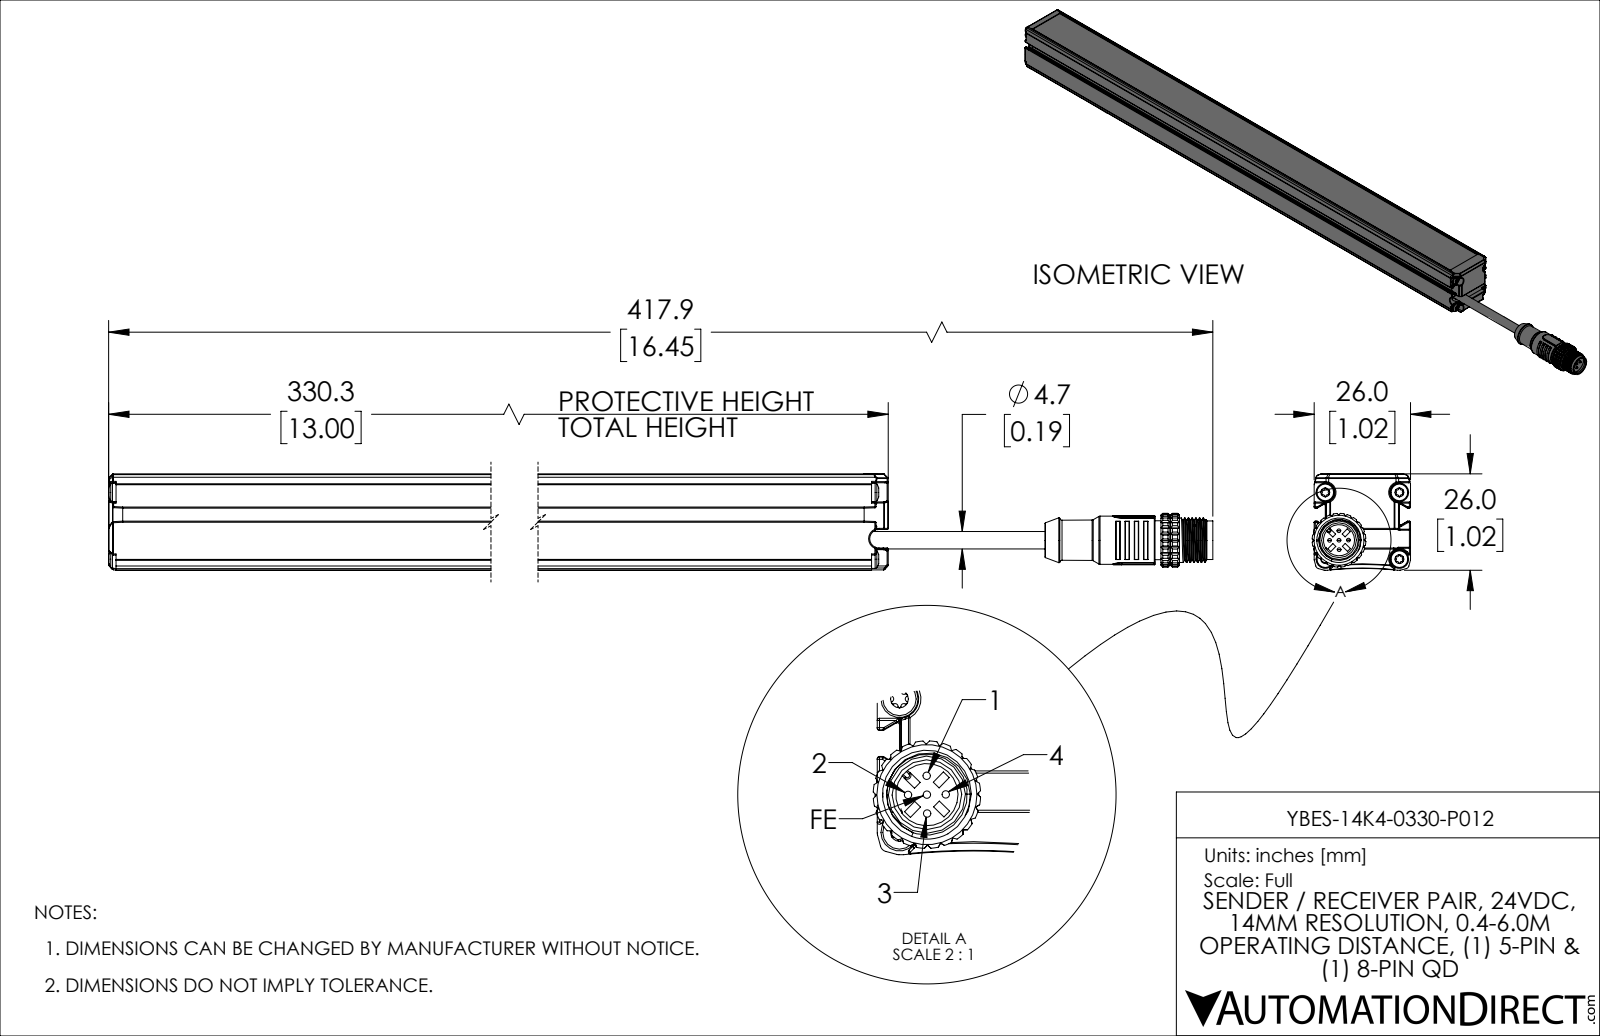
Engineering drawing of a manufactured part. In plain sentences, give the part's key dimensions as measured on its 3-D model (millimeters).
The part is named "YBES-14K4-0330-P012_REV1". Its 3-D file was written by "SolidWorks 2019 (AUTOMOTIVE_DESIGN)". It is 2 solids with 1937 faces: 729 planar, 727 cylindrical and 481 other. Overall it measures 417.9 by 26.5 by 26 millimeters. Its volume is 82 070 cubic millimeters and its surface area 89 030 square millimeters. Round holes: 4 of diameter 2.4, 4 of diameter 2.5, 4 of diameter 3.7, 4 of diameter 5, 1 of diameter 4.8, 1 of diameter 5.9, 1 of diameter 8.4, 1 of diameter 9, 1 of diameter 9.6. Round bosses or shafts: 5 of diameter 1, 5 of diameter 0.9, 4 of diameter 3.2, 4 of diameter 2.5, 4 of diameter 1.3, 2 of diameter 1.5, 1 of diameter 13.5, 1 of diameter 13. Partial cylindrical surfaces (rounded edges, fillets, slot ends): 153 of radius 0.2, 115 of radius 0.3, 24 of radius 0.2, 24 of radius 0.4, 18 of radius 1, 16 of radius 0.4, 10 of radius 0.2, 7 of radius 0.5. The main face-to-face distances are 3, 1.5, 1.8, 21.2, 26, 18.2, 1.2, 0.4, 23, 4.8. The hole center spacings are 18, 20, 26.9, 6.3, 13.4, 17.1, 20.8.
